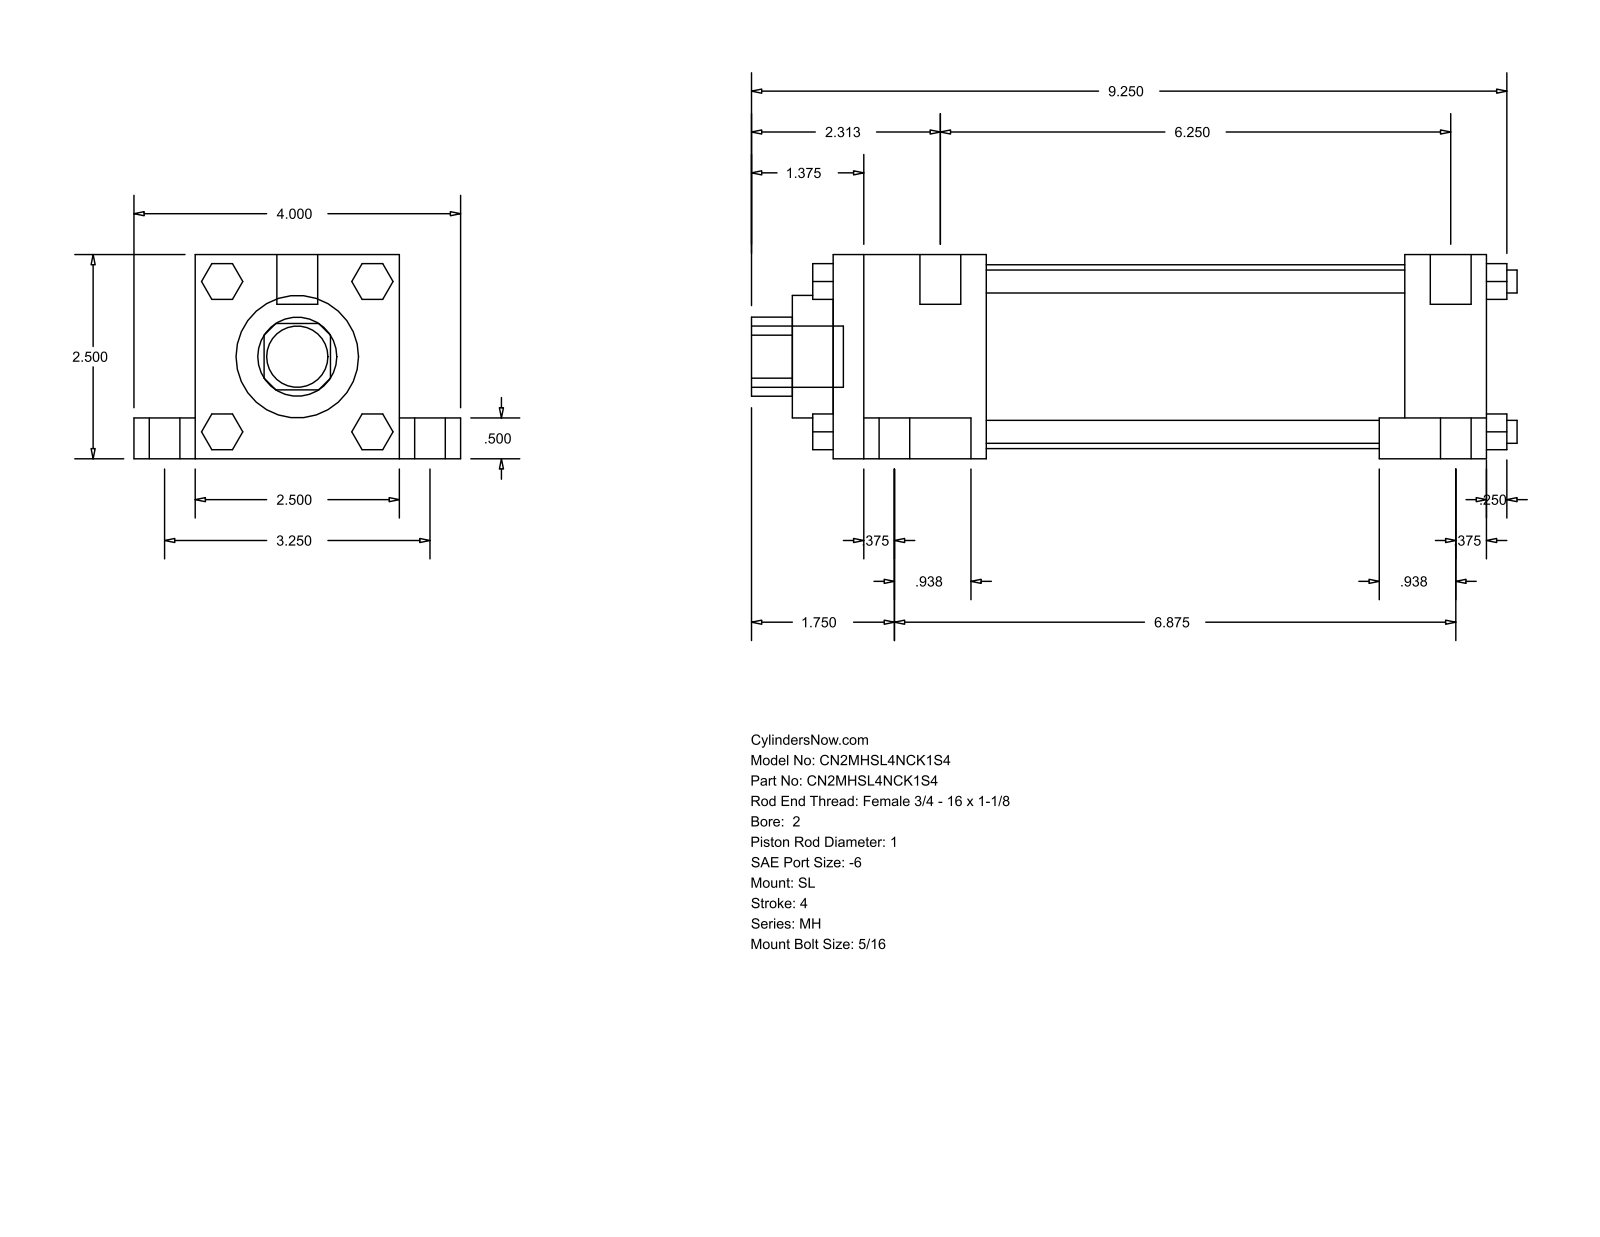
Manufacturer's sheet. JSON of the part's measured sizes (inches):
{"part_name": "MH_SL__0200_1", "step_written_by": "GSSL Pune (CONFIG_CONTROL_DESIGN)", "units": "inches", "bodies": {"solids": 0, "faces": 148, "planar": 112, "cylindrical": 36, "other": 0}, "overall_size": [9.375, 4, 2.5], "round_holes": [[1, 1], [1.5, 1], [2.25, 1]], "round_bosses_or_shafts": [[0.625, 4], [0.375, 4], [0.281, 4], [0.219, 4], [0.5, 2], [0.75, 1]], "partial_cylinders_radius": [[0.484, 1]], "face_to_face_distances": [2.5, 8, 0.5, 0.75, 2, 3.25, 0.375, 1, 7, 1.875]}
